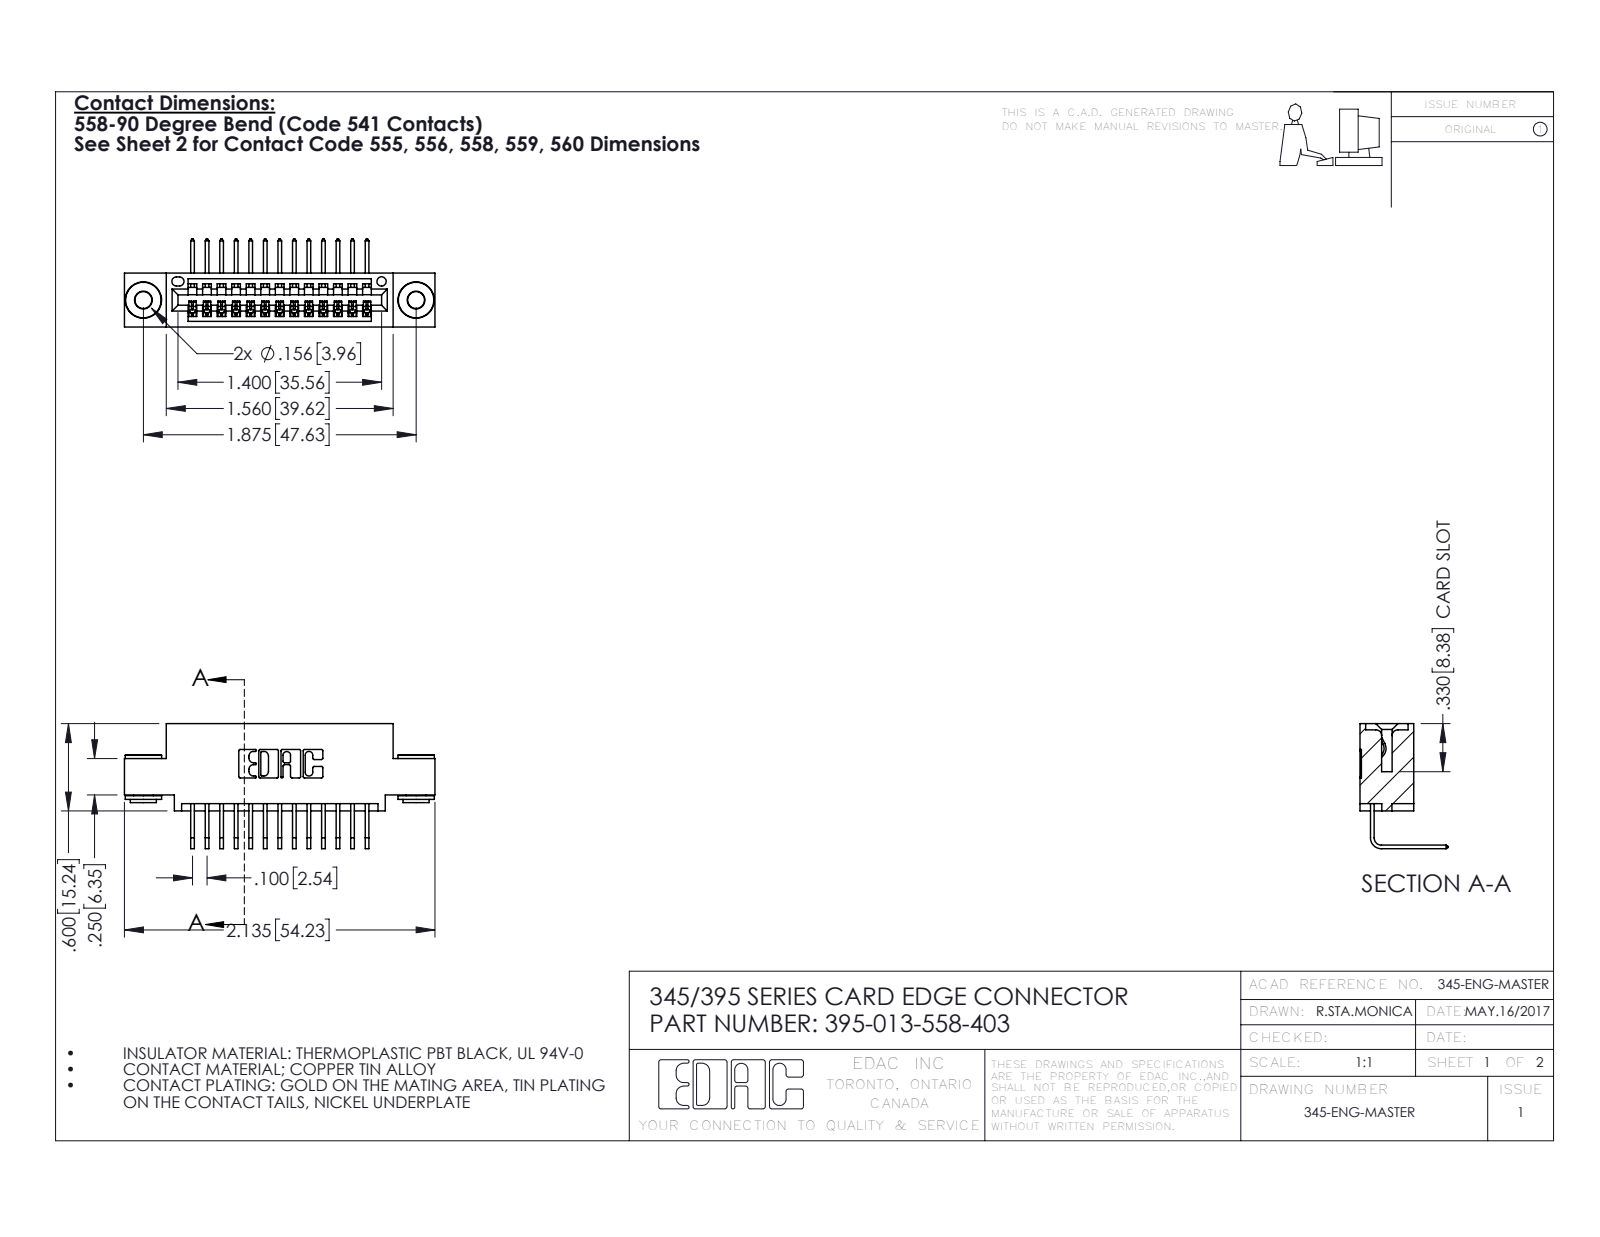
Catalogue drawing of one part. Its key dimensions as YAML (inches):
part_name: "345-292-001_558 Tail - 2; 345 Part_0.110 Offset - 0.156 Dia-TH; 395-013-558-403; 345-250-002_345-250-002-102"
step_written_by: "SolidWorks 2016 (CONFIG_CONTROL_DESIGN)"
units: inches
bodies: {solids: 16, faces: 948, planar: 640, cylindrical: 300, other: 8}
overall_size: [2.135, 0.859, 0.605]
volume: 0.299
surface_area: 10.34
round_holes:
  - {diameter: 0.116, count: 2}
  - {diameter: 0.156, count: 2}
  - {diameter: 0.064, count: 1}
round_bosses_or_shafts:
  - {diameter: 0.25, count: 2}
  - {diameter: 0.18, count: 2}
  - {diameter: 0.136, count: 2}
partial_cylinders:
  - {radius: 0.006, count: 26}
  - {radius: 0.01, count: 22}
  - {radius: 0.007, count: 6}
  - {radius: 0.031, count: 6}
  - {radius: 0.026, count: 3}
  - {radius: 0.031, count: 2}
  - {radius: 0.04, count: 2}
  - {radius: 0.014, count: 1}
face_to_face_distances: [0.072, 0.298, 0.2, 0.37, 0.025, 0.098, 0.272, 0.1, 0.225, 0.16]
hole_center_spacings: [0.27, 1.643, 1.875]
